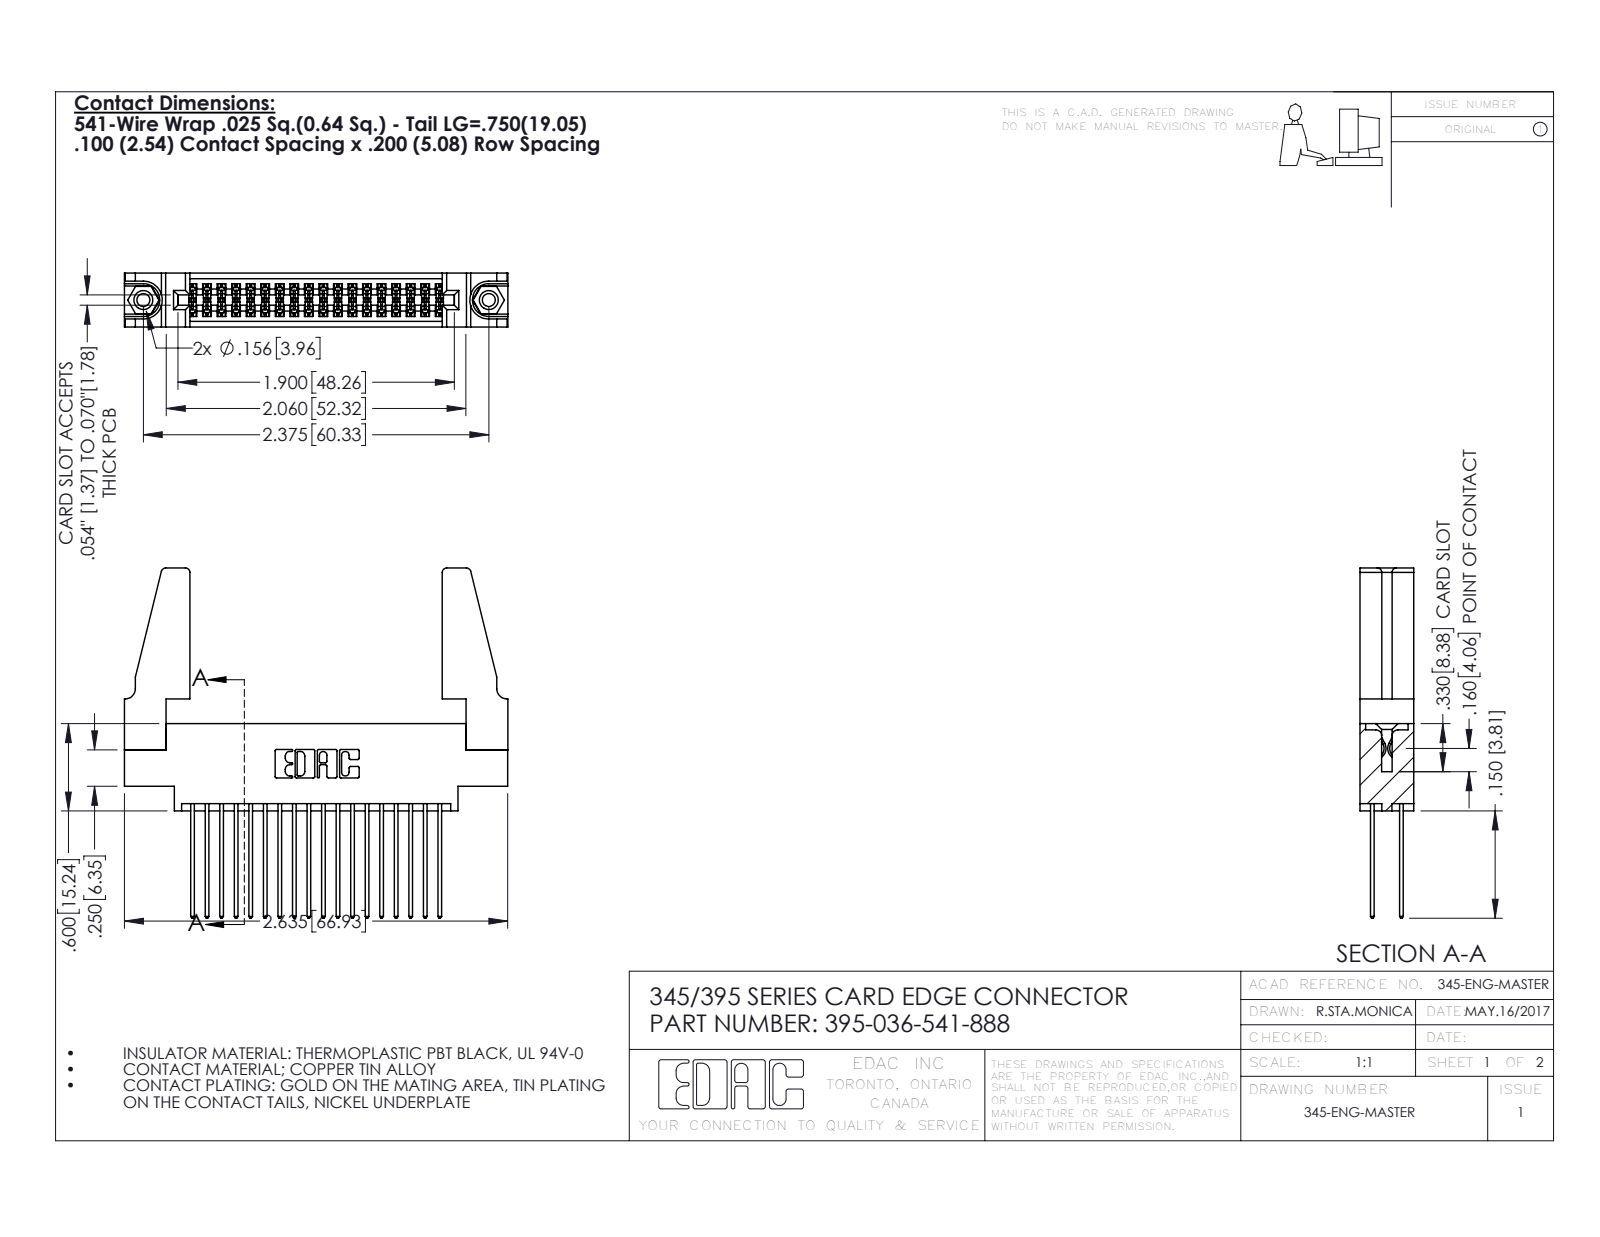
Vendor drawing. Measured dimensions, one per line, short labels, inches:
name: 345-292-001_345-293-141; 345-250-001_345-250-001-102; 345-220-078_345-220-088; 395-036-541-888 (+1 more)
written by: SolidWorks 2016 (CONFIG_CONTROL_DESIGN)
unit: in
bodies: 41 solids, 2054 faces (1344 planar, 694 cylindrical, 16 other)
size: 2.636 × 2.407 × 0.37
volume: 0.587 in³; area: 20.45 in²
holes: 2× ⌀0.089, 2× ⌀0.125, 2× ⌀0.156, 1× ⌀0.064
bosses: 2× ⌀0.155
rounds: 54× R0.006, 36× R0.01, 22× R0.01, 8× R0.03, 6× R0.007, 6× R0.031, 3× R0.026, 2× R0.014
face distances: 0.072, 0.298, 0.37, 0.2, 0.098, 0.272, 0.025, 0.225, 0.175, 0.15
hole spacings: 0.27, 2.141, 2.375
